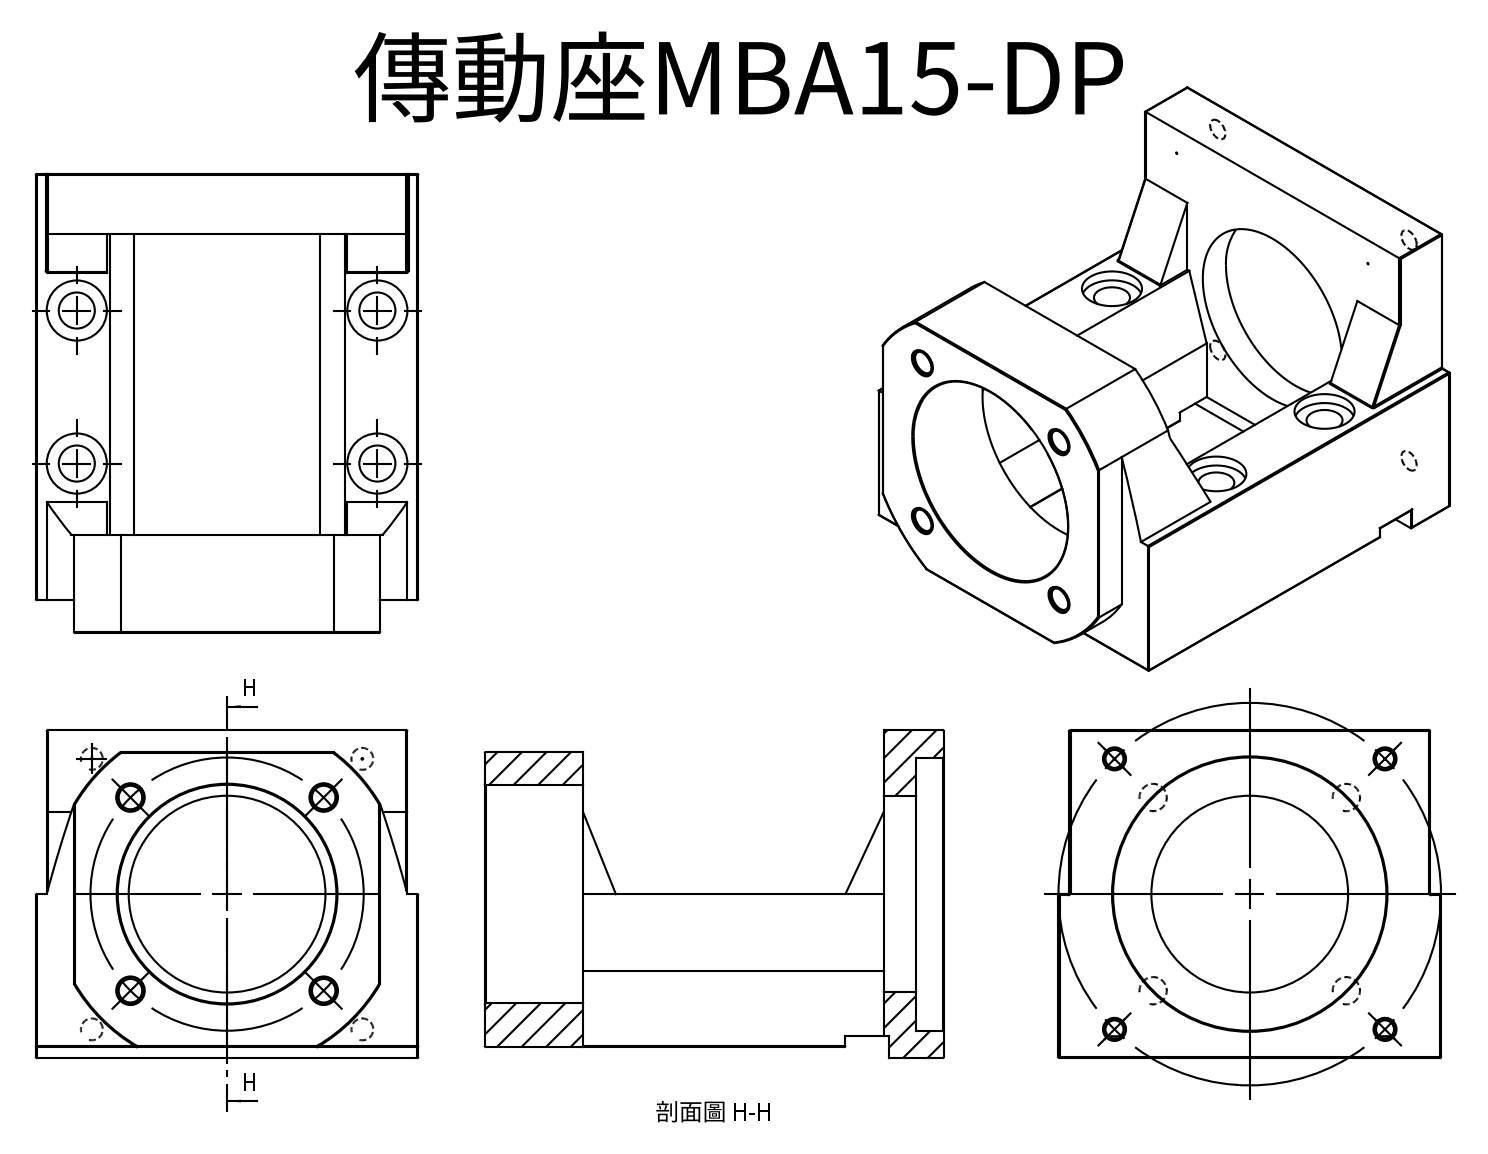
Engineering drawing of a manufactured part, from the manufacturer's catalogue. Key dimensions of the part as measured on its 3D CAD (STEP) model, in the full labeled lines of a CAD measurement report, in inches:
STEP written by: SolidWorks 2011 (CONFIG_CONTROL_DESIGN)
Units: inches
Bodies: 1 solid, 226 faces (41 planar, 97 cylindrical, 88 other)
Overall size (bounding box): 3.307 × 2.756 × 2.362
Volume: 6.827 in³ · Surface area: 50.62 in²
Round holes (diameter × count): ⌀0.13 ×4, ⌀0.169 ×4, ⌀0.26 ×4, ⌀0.433 ×4, ⌀0.228 ×2, ⌀0.236 ×2, ⌀1.417 ×1, ⌀1.575 ×1, ⌀1.969 ×1
Partial cylindrical surfaces — rounded edges, fillets, slot ends (radius × count): R0.008 ×41, R9.843 ×2, R1.28 ×1
Main face-to-face distances: 0.709, 0.433, 2.756, 2.874, 0.079, 0.197, 2.047, 0.236, 3.307, 1.181
Hole centre spacings: 1.693, 0.394, 0.551, 0.984, 1.378, 1.392, 1.949, 2.234
